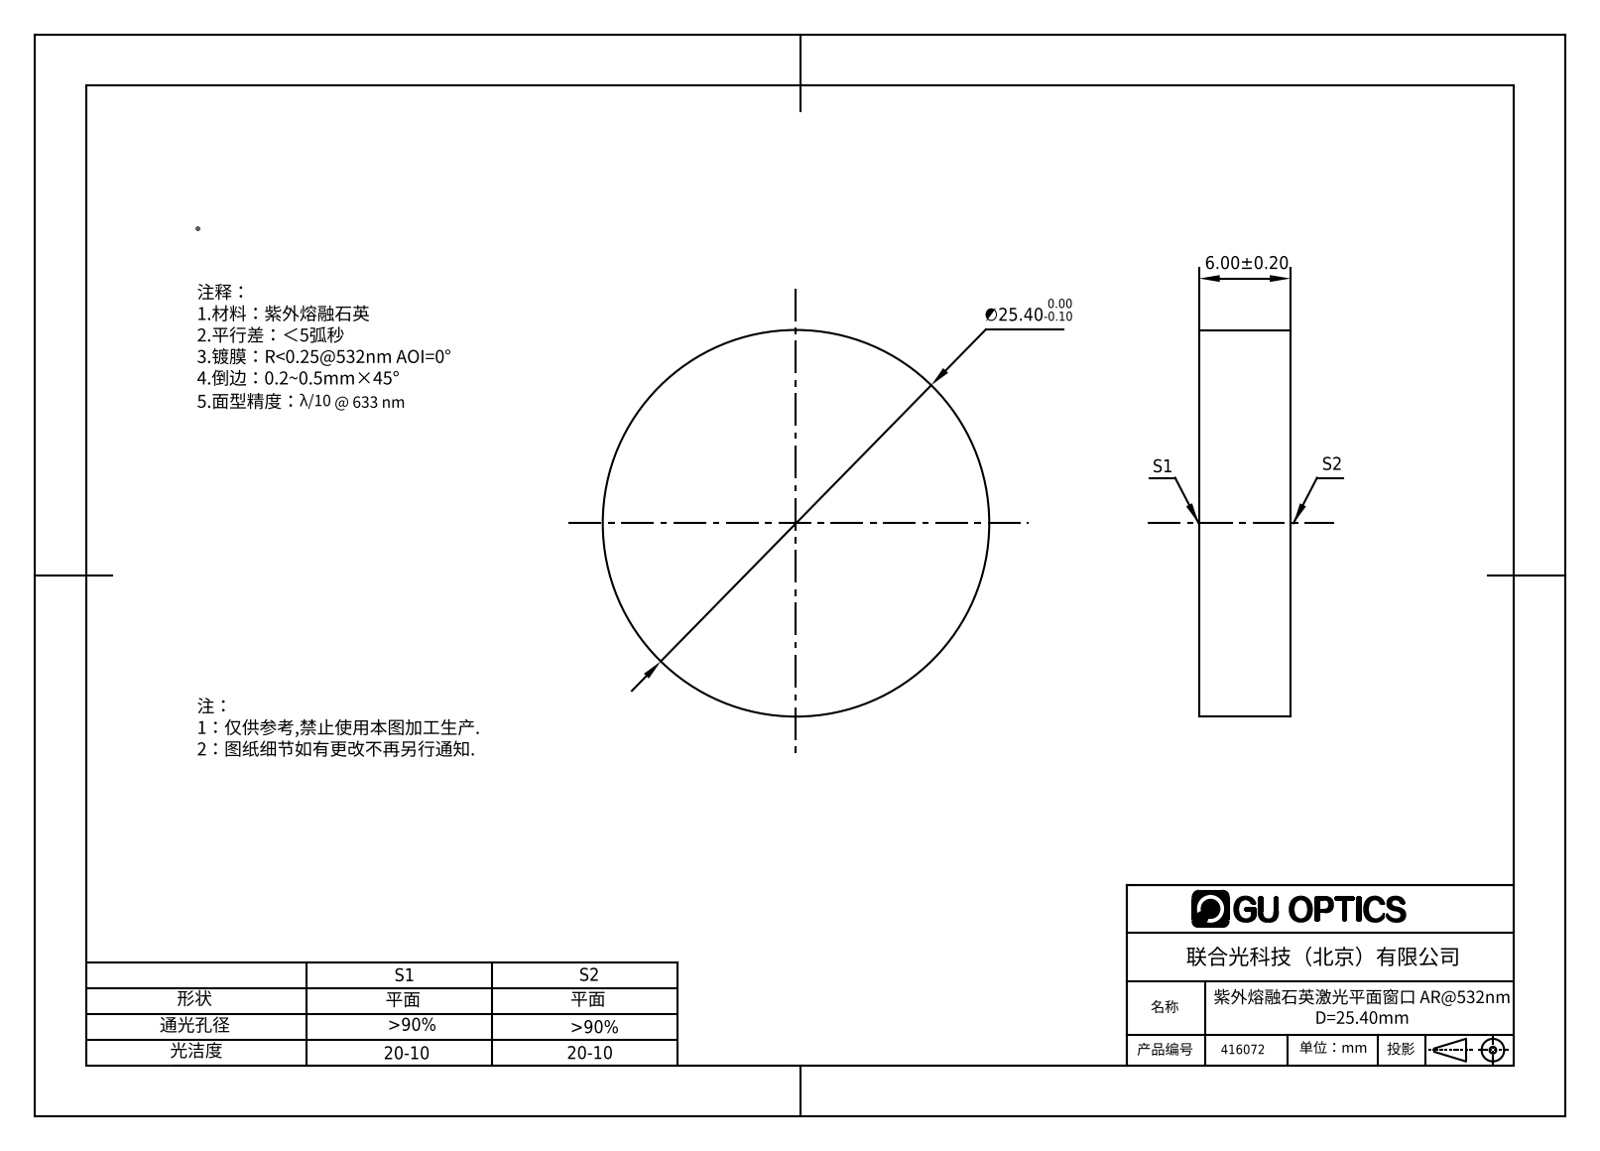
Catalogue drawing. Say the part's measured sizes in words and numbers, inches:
The part is named "416006". Its 3-D file was written by "SolidWorks 2016 (CONFIG_CONTROL_DESIGN)". It is 1 solid with 4 faces: 2 planar, 2 cylindrical and 0 other. Overall it measures 1 by 1 by 0.236 inches. Its volume is 0.186 cubic inches and its surface area 2.313 square inches. Round bosses or shafts: 1 of diameter 1. The main face-to-face distances are 0.236.
